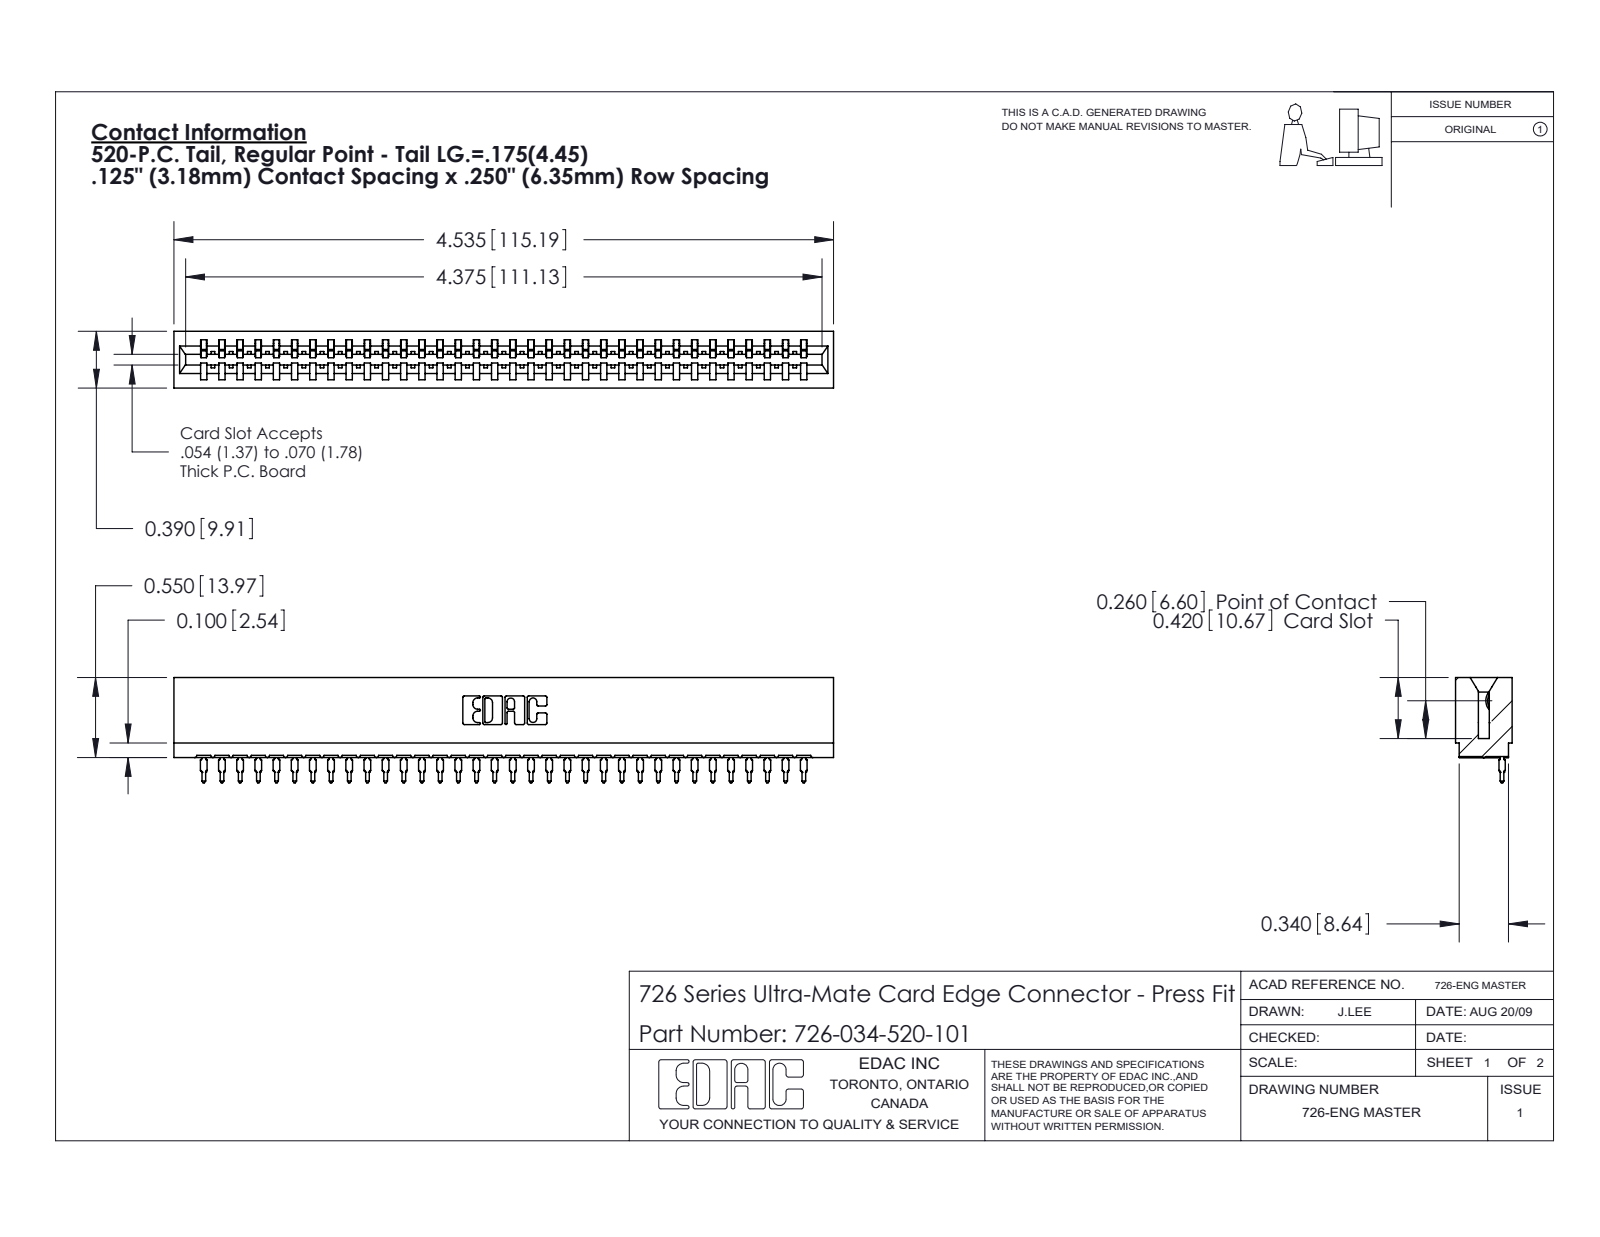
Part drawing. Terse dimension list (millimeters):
name: 726 Part_.515 Slot Depth - 01; 726-034-520-101; 746-292-001_520
written by: SolidWorks 2020 (CONFIG_CONTROL_DESIGN)
unit: mm
bodies: 35 solids, 3769 faces (2197 planar, 688 cylindrical, 884 other)
size: 115.2 × 18.4 × 9.9
volume: 10 300 mm³; area: 15 340 mm²
rounds: 68× R0.5, 35× R0.4, 22× R0.3, 6× R0.2, 6× R0.8, 4× R0.1, 4× R0.3, 3× R0.7
face distances: 1.4, 8.5, 9.9, 0.6, 7.8, 6.4, 7, 9.3, 0.8, 4.4
